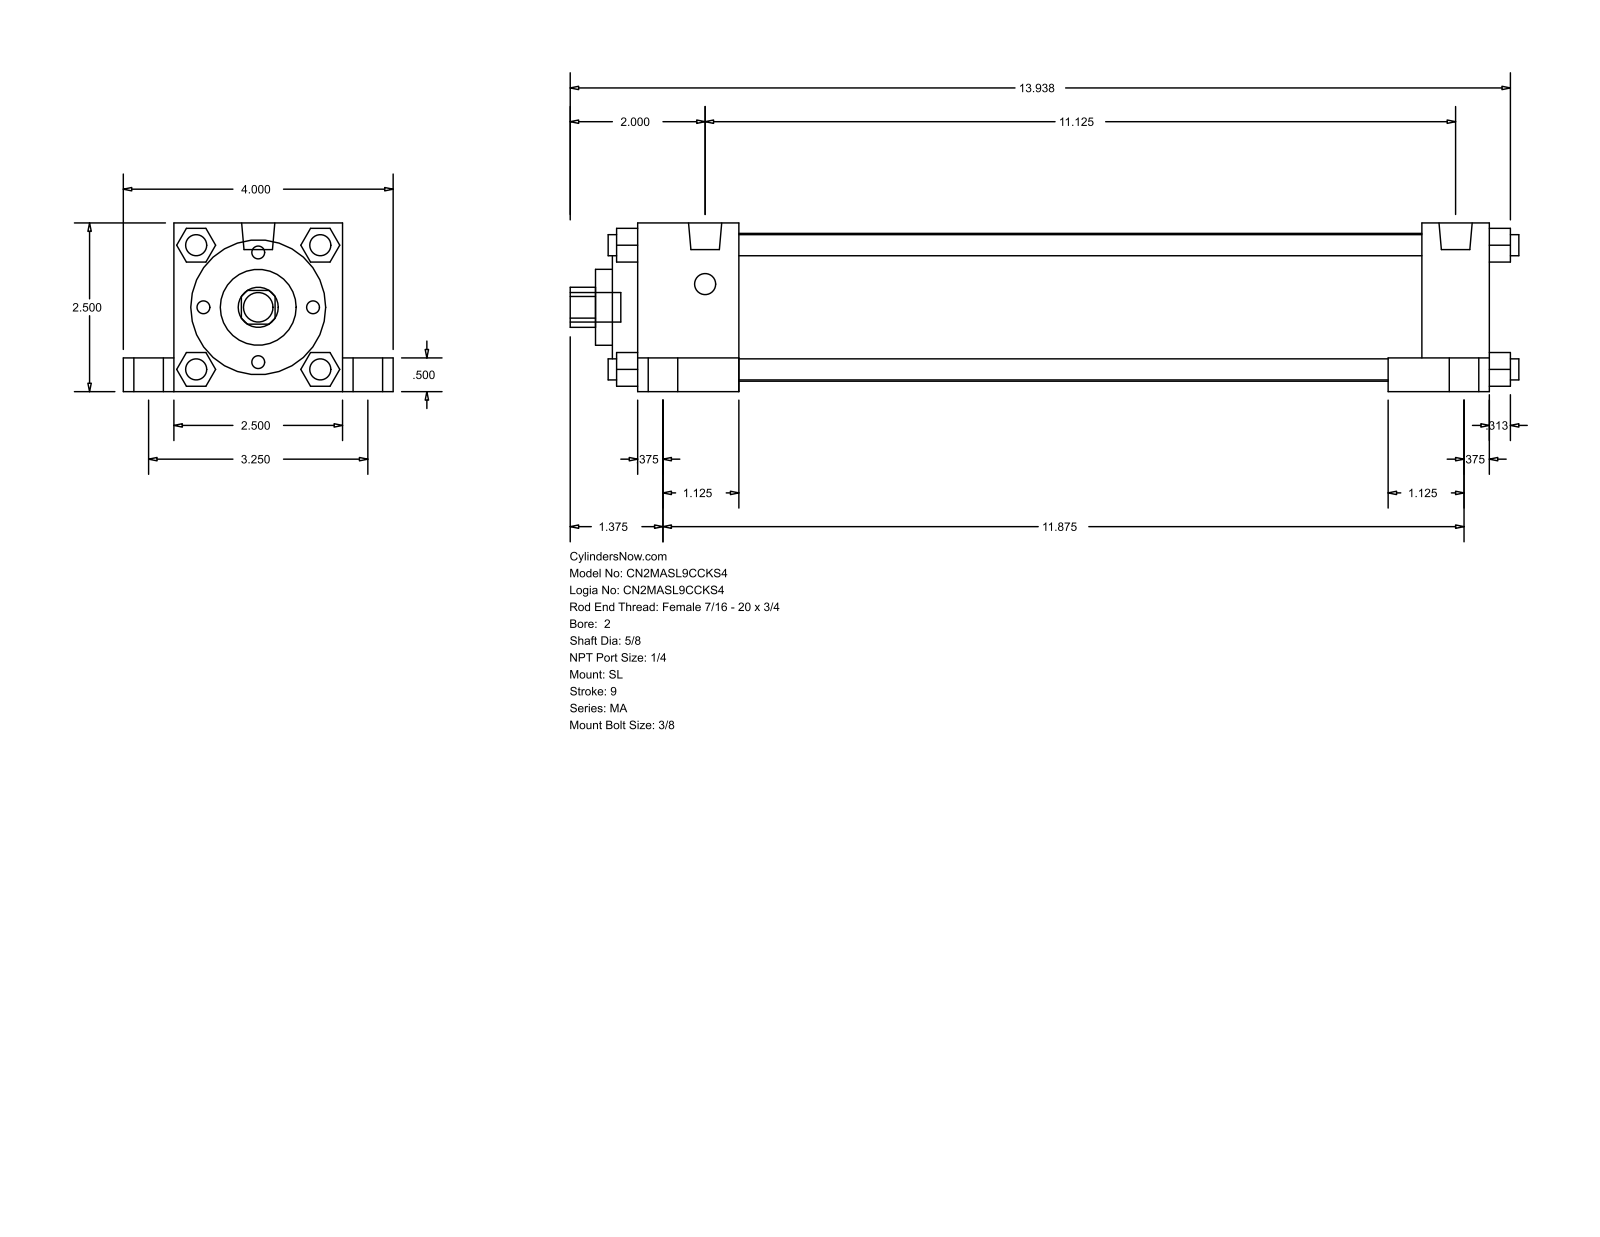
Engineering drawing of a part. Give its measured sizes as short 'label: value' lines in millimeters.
name: MA_SL__0200_0.625
written by: GSSL Pune (CONFIG_CONTROL_DESIGN)
unit: mm
bodies: 0 solids, 150 faces (113 planar, 37 cylindrical, 0 other)
size: 357.19 × 101.6 × 63.5
holes: 1× ⌀15.88, 1× ⌀28.57, 1× ⌀50.8, 1× ⌀55.63
bosses: 8× ⌀7.94, 5× ⌀11.11, 4× ⌀17.46, 2× ⌀12.49
rounds: 1× R7.54
face distances: 63.5, 12.7, 9.52, 19.05, 82.55, 38.1, 50.8, 320.67, 282.57, 295.28
